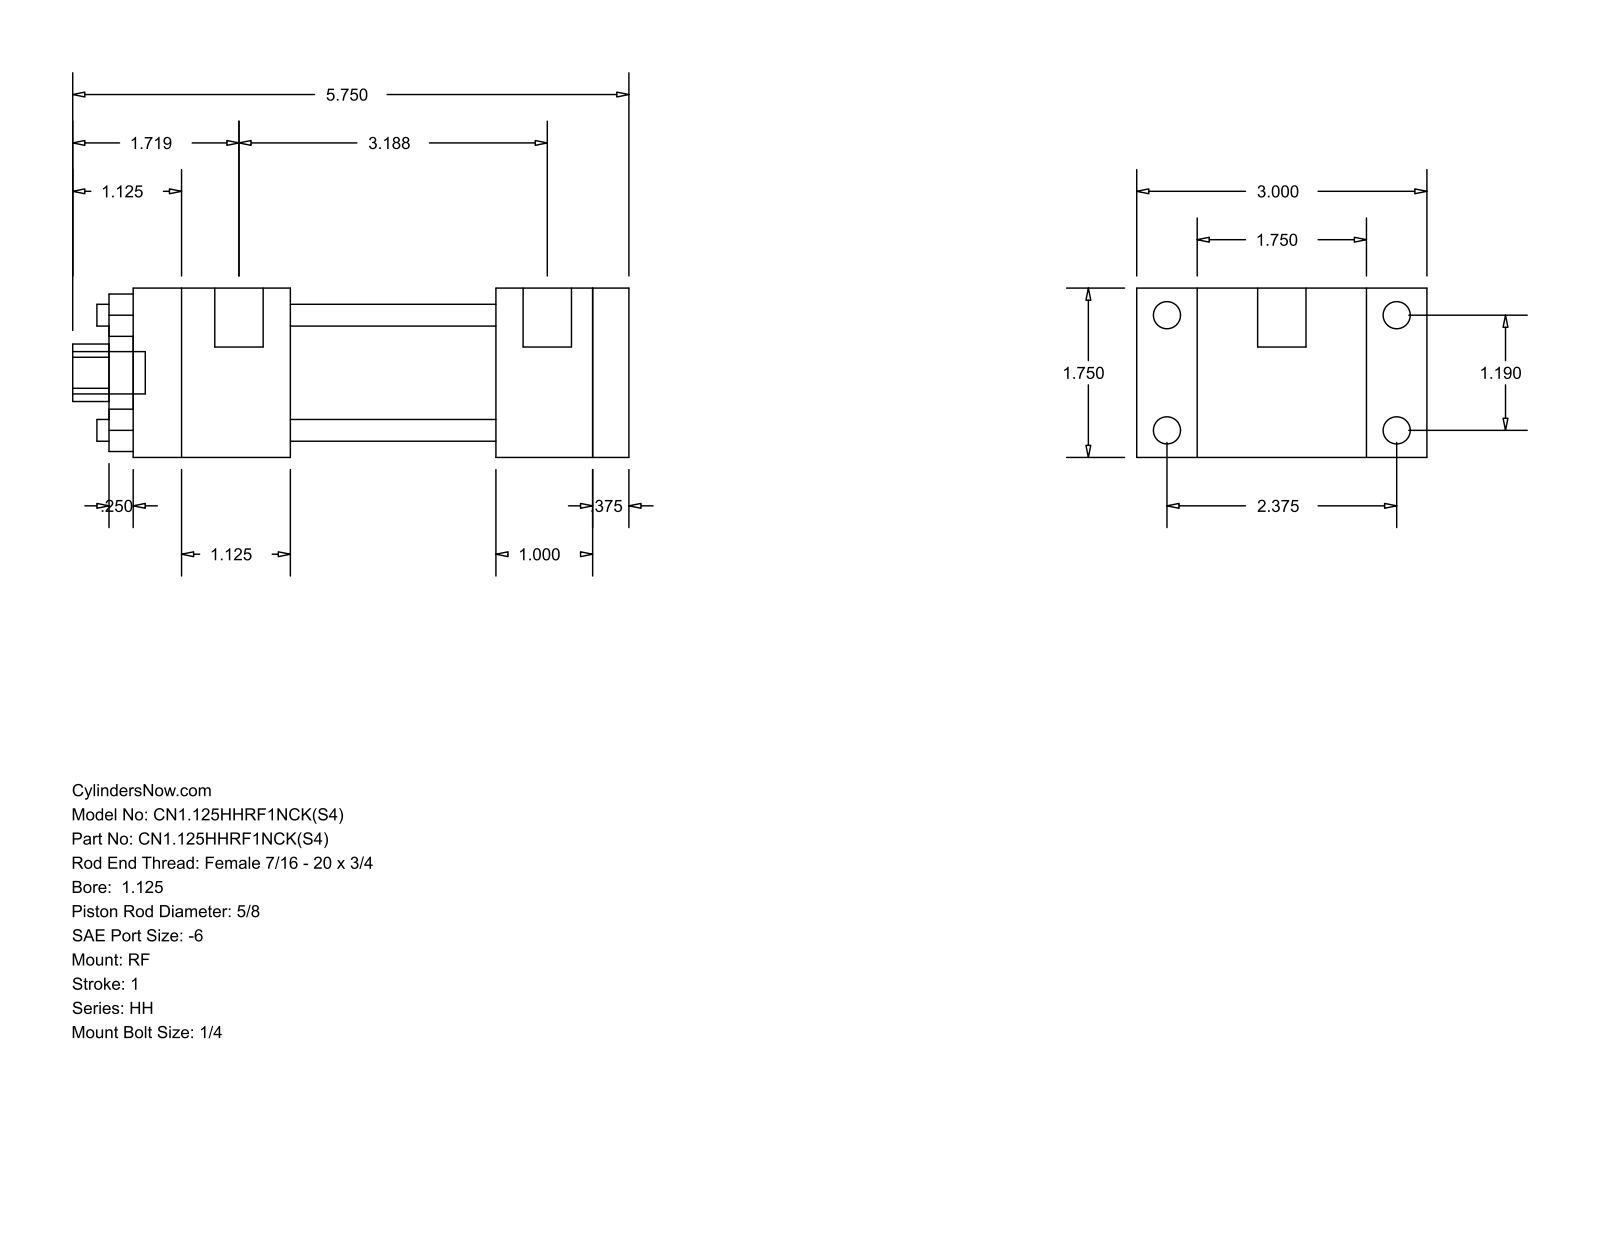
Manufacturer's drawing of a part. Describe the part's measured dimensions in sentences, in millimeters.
The part is named "HH_RF__0112_0.625". Its 3-D file was written by "GSSL Pune (CONFIG_CONTROL_DESIGN)". It is 0 solids with 92 faces: 64 planar, 28 cylindrical and 0 other. Overall it measures 146.05 by 76.2 by 44.45 millimeters. Round holes: 4 of diameter 5.71, 1 of diameter 15.88, 1 of diameter 28.57, 1 of diameter 34.92. Round bosses or shafts: 4 of diameter 7.14, 4 of diameter 5.56, 2 of diameter 12.7, 1 of diameter 11.11. Partial cylindrical surfaces (rounded edges, fillets, slot ends): 1 of radius 7.54. The main face-to-face distances are 44.46, 9.52, 15.87, 79.38, 88.9, 53.97, 25.41, 34.93, 41.27, 95.24. The hole center spacings are 21.37, 30.22, 42.74.
